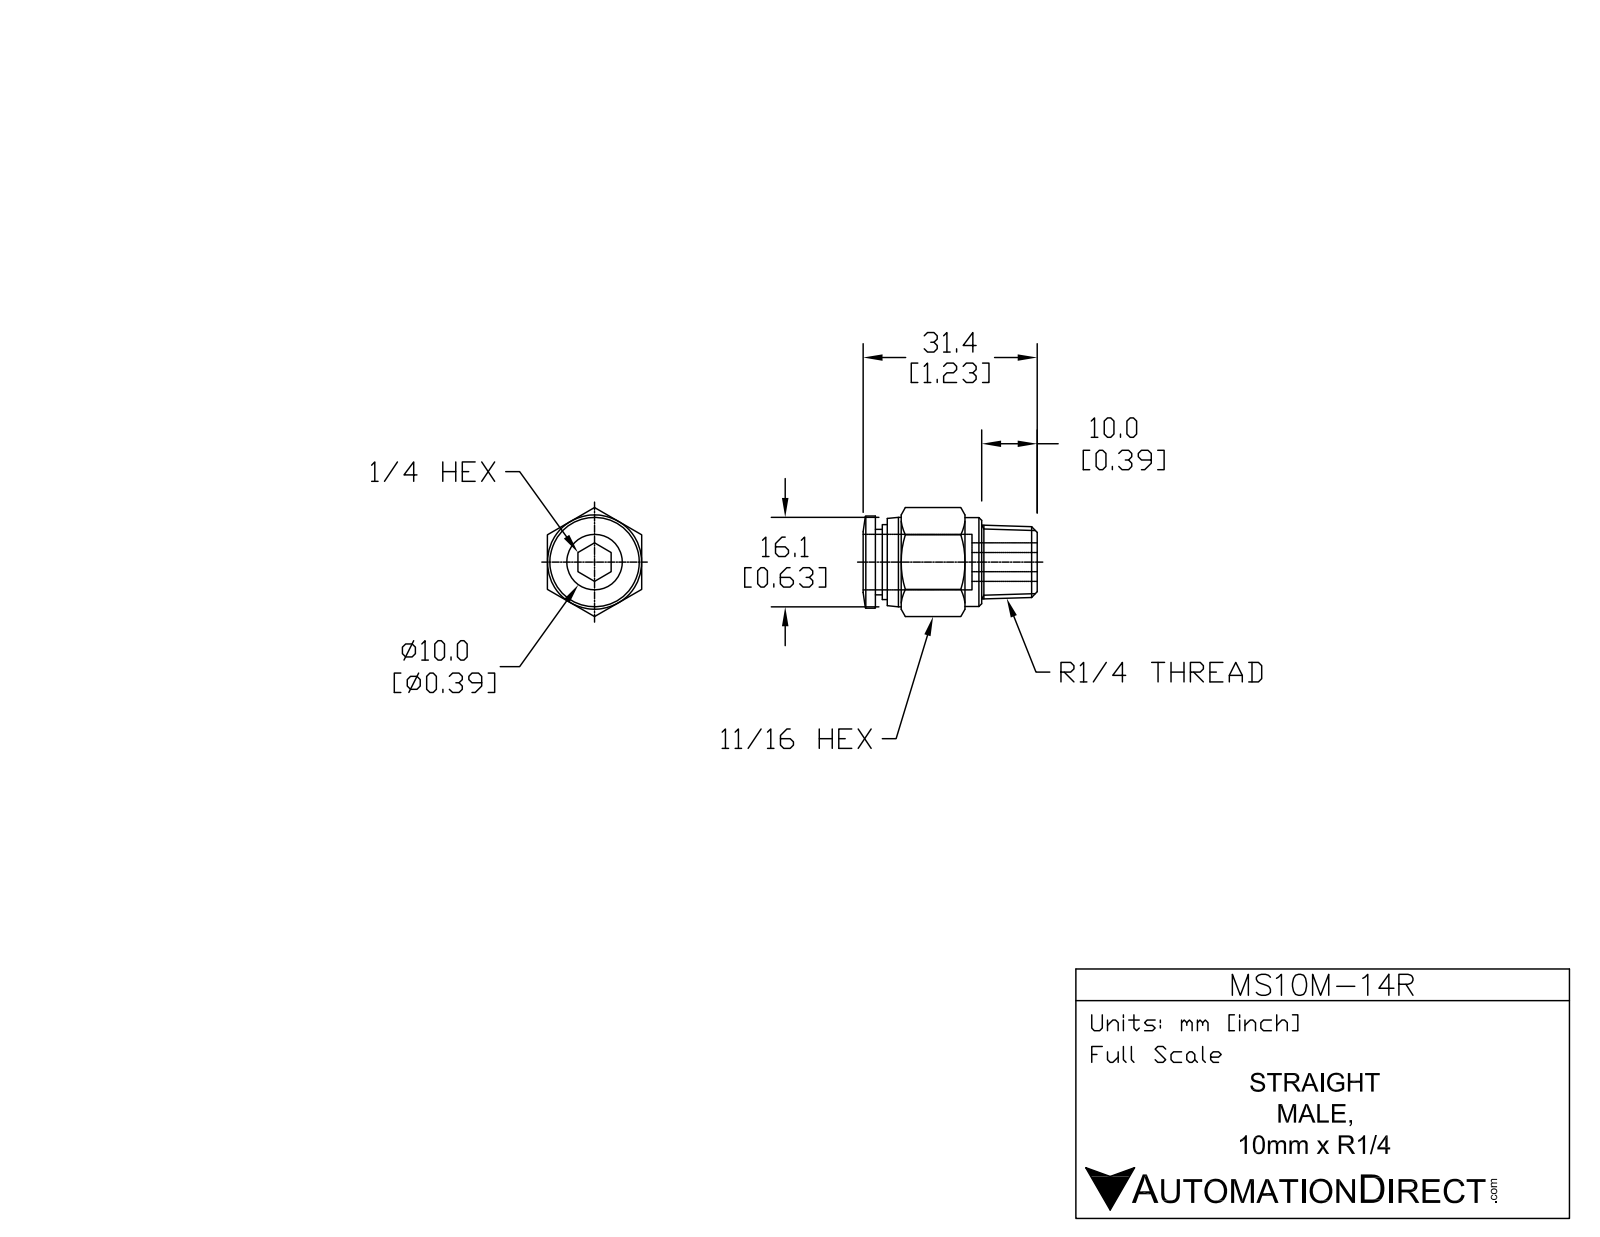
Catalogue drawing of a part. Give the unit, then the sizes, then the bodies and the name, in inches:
Units: inches
Overall size (bounding box): 1.234 × 0.773 × 0.669
Round holes (diameter × count): ⌀0.276 ×1, ⌀0.406 ×1
Round bosses / shafts (diameter × count): ⌀0.654 ×1, ⌀0.634 ×1, ⌀0.63 ×1, ⌀0.531 ×1, ⌀0.465 ×1
Main face-to-face distances: 0.669, 0.049, 0.636, 1.148, 1.063, 0.085, 0.463, 0.6, 0.685, 0.394
Volume: 0.238 in³ · Surface area: 4.621 in²
Bodies: 1 solid, 57 faces (15 planar, 14 cylindrical, 28 other)
Part name (STEP PRODUCT): MS10M-14R
STEP written by: SolidWorks 2015 (AUTOMOTIVE_DESIGN)
